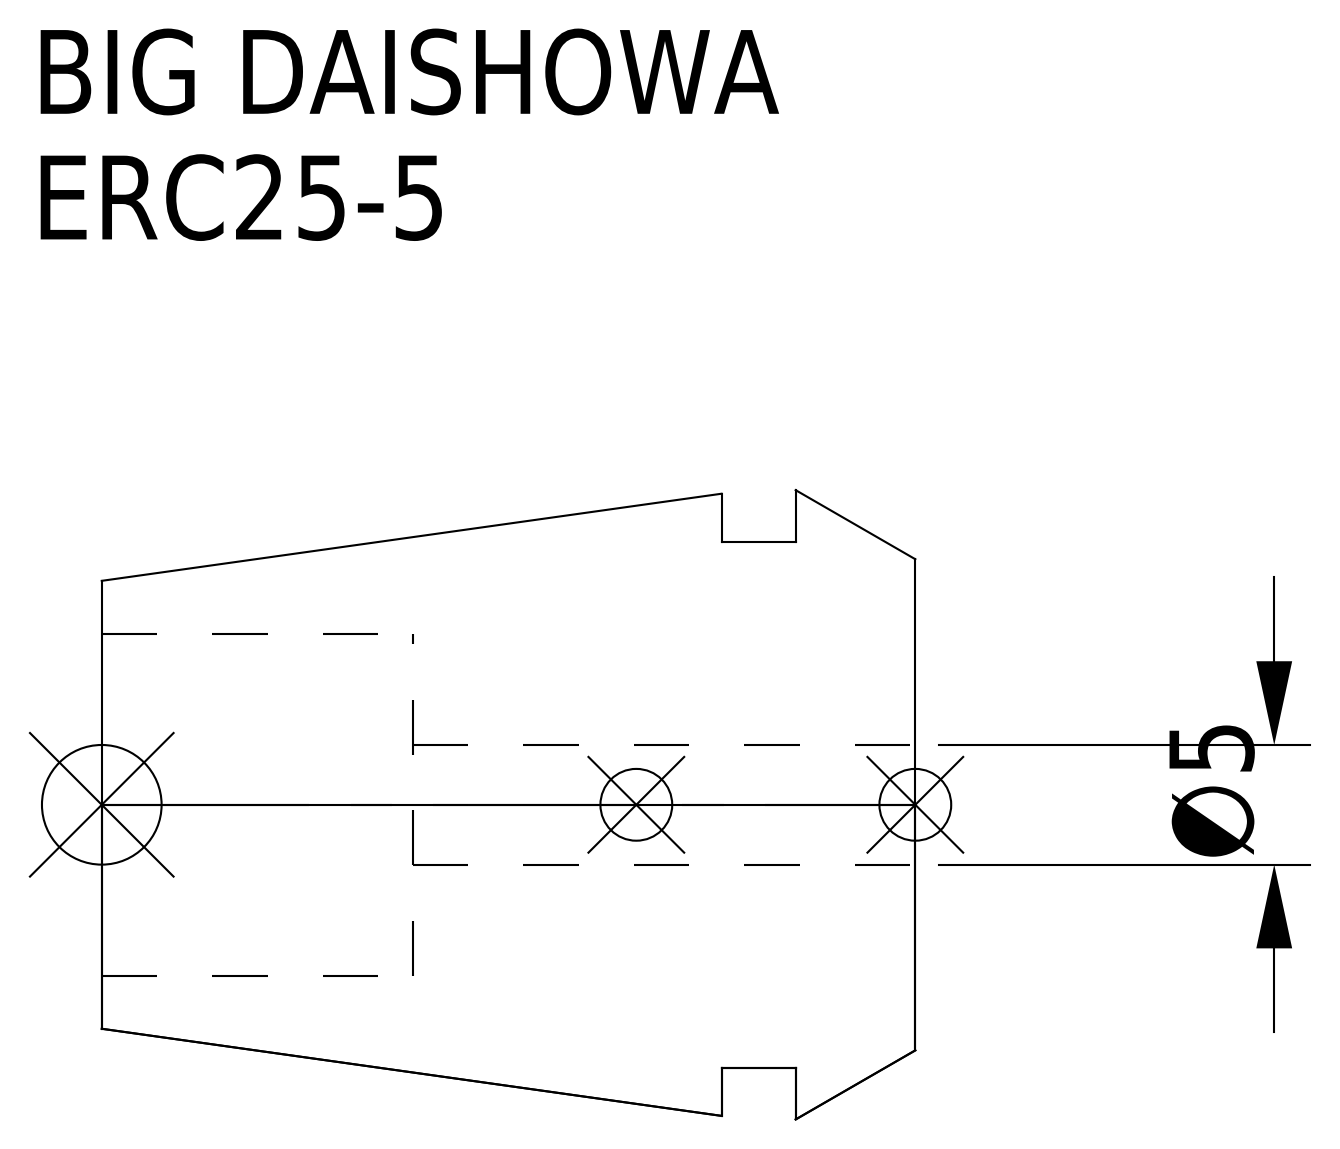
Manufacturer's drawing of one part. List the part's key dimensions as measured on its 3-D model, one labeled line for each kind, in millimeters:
Part name (STEP PRODUCT): ERC25-5
STEP written by: CREO PARAMETRIC BY PTC INC, 2016380 (AUTOMOTIVE_DESIGN)
Units: millimetres
Bodies: 1 solid, 15 faces (5 planar, 6 cylindrical, 4 other)
Overall size (bounding box): 34 × 26.3 × 26.3
Volume: 11 103 mm³ · Surface area: 4 271 mm²
Round holes (diameter × count): ⌀5 ×1, ⌀14.3 ×1
Round bosses / shafts (diameter × count): ⌀22 ×1
Main face-to-face distances: 5, 8.1, 3.1, 21, 16, 12.9, 34, 29, 25.9, 13
